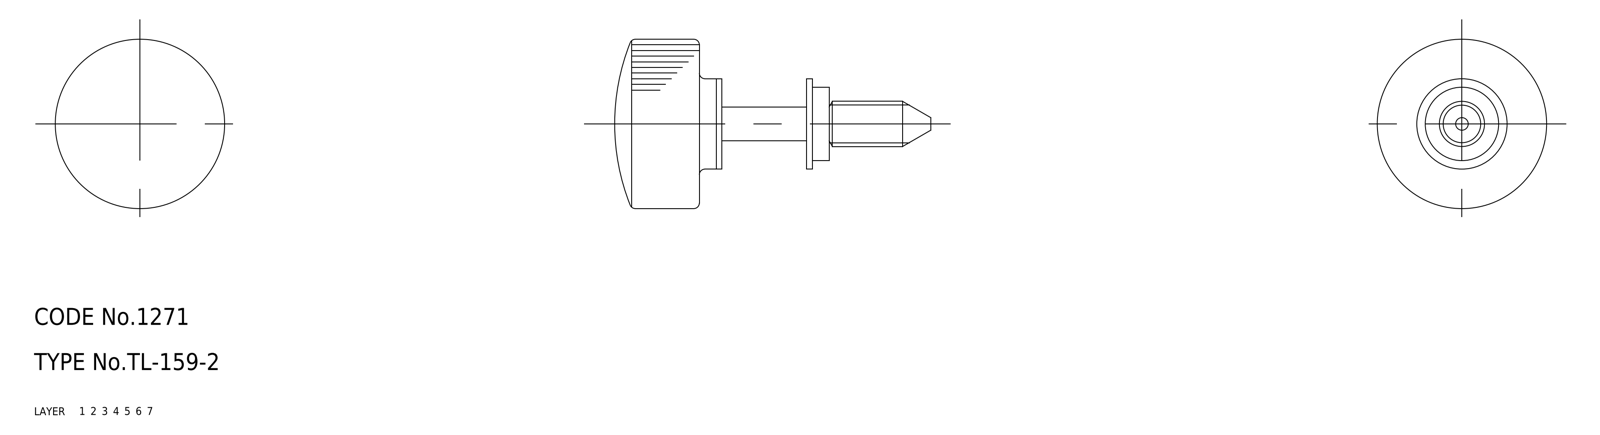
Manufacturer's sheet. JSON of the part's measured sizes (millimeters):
{"part_name": "washer_B; washer_A; knob; collar (+1 more)", "step_written_by": "CADfix (AUTOMOTIVE_DESIGN)", "units": "millimeters", "bodies": {"solids": 4, "faces": 40, "planar": 0, "cylindrical": 0, "other": 40}, "overall_size": [56, 30, 30], "volume_mm3": 12152, "surface_area_mm2": 4649}
